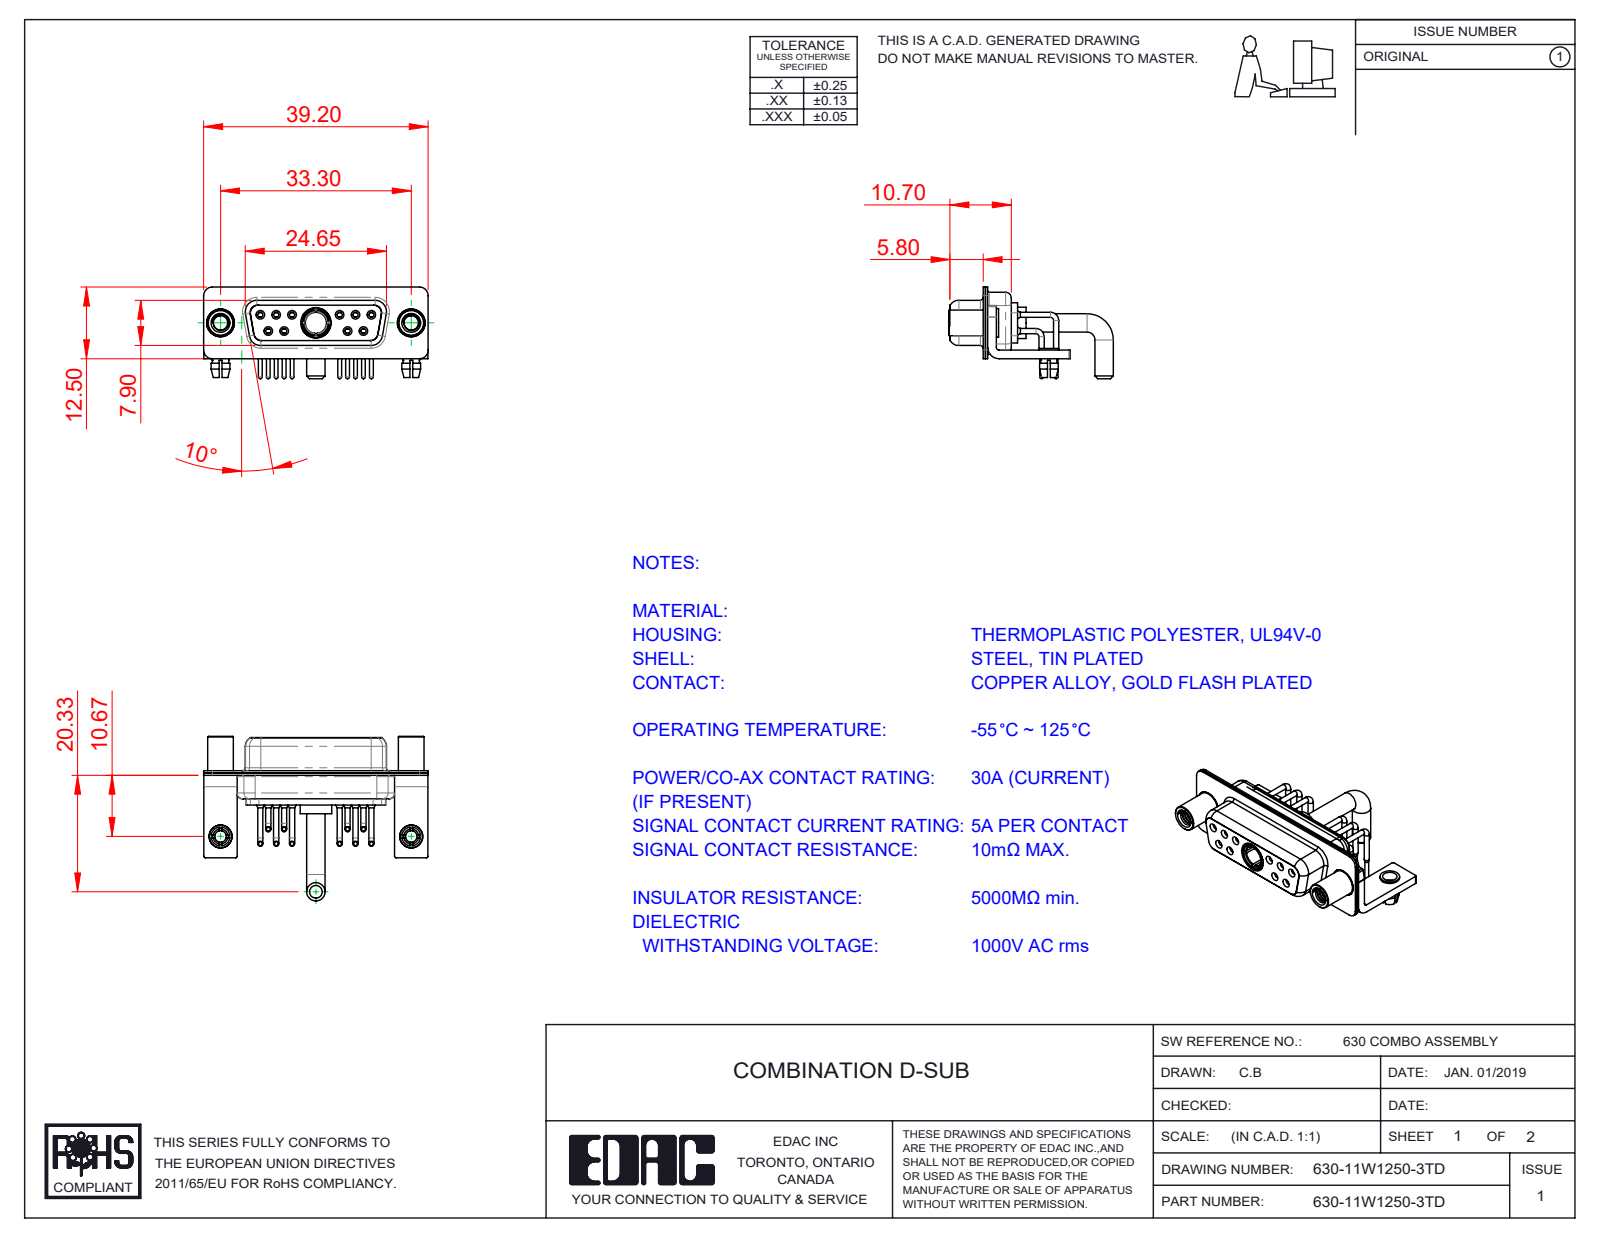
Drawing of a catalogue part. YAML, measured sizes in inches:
part_name: "630Combo Stabilizer Bracket; Power Socket_Ext 30A RA; 630Combo Shell Rear_15 Contacts; 630Combo Threaded Standoff_D (+6 more)"
step_written_by: "SolidWorks 2020 (CONFIG_CONTROL_DESIGN)"
units: inches
bodies: {solids: 21, faces: 1077, planar: 316, cylindrical: 496, other: 265}
overall_size: [1.543, 1.131, 0.63]
volume: 0.192
surface_area: 11.62
round_holes:
  - {diameter: 0.079, count: 12}
  - {diameter: 0.035, count: 10}
  - {diameter: 0.043, count: 10}
  - {diameter: 0.059, count: 10}
  - {diameter: 0.067, count: 6}
  - {diameter: 0.063, count: 4}
  - {diameter: 0.098, count: 4}
  - {diameter: 0.191, count: 3}
  - {diameter: 0.126, count: 2}
  - {diameter: 0.157, count: 2}
  - {diameter: 0.159, count: 2}
  - {diameter: 0.146, count: 1}
round_bosses_or_shafts:
  - {diameter: 0.035, count: 10}
  - {diameter: 0.026, count: 10}
  - {diameter: 0.063, count: 6}
  - {diameter: 0.197, count: 2}
  - {diameter: 0.195, count: 2}
  - {diameter: 0.189, count: 2}
  - {diameter: 0.177, count: 2}
  - {diameter: 0.157, count: 2}
partial_cylinders:
  - {radius: 0.01, count: 16}
  - {radius: 0.059, count: 16}
  - {radius: 0.079, count: 13}
  - {radius: 0.053, count: 12}
  - {radius: 0.063, count: 8}
  - {radius: 0.02, count: 5}
  - {radius: 0.024, count: 4}
  - {radius: 0.026, count: 4}
face_to_face_distances: [0.016, 0.031, 0.018, 0.055, 0.333, 0.059, 0.071, 0.35, 0.244, 0.091]
hole_center_spacings: [0.124, 0.109, 0.545, 0.436, 0.654, 0.198, 0.198, 0.218]
